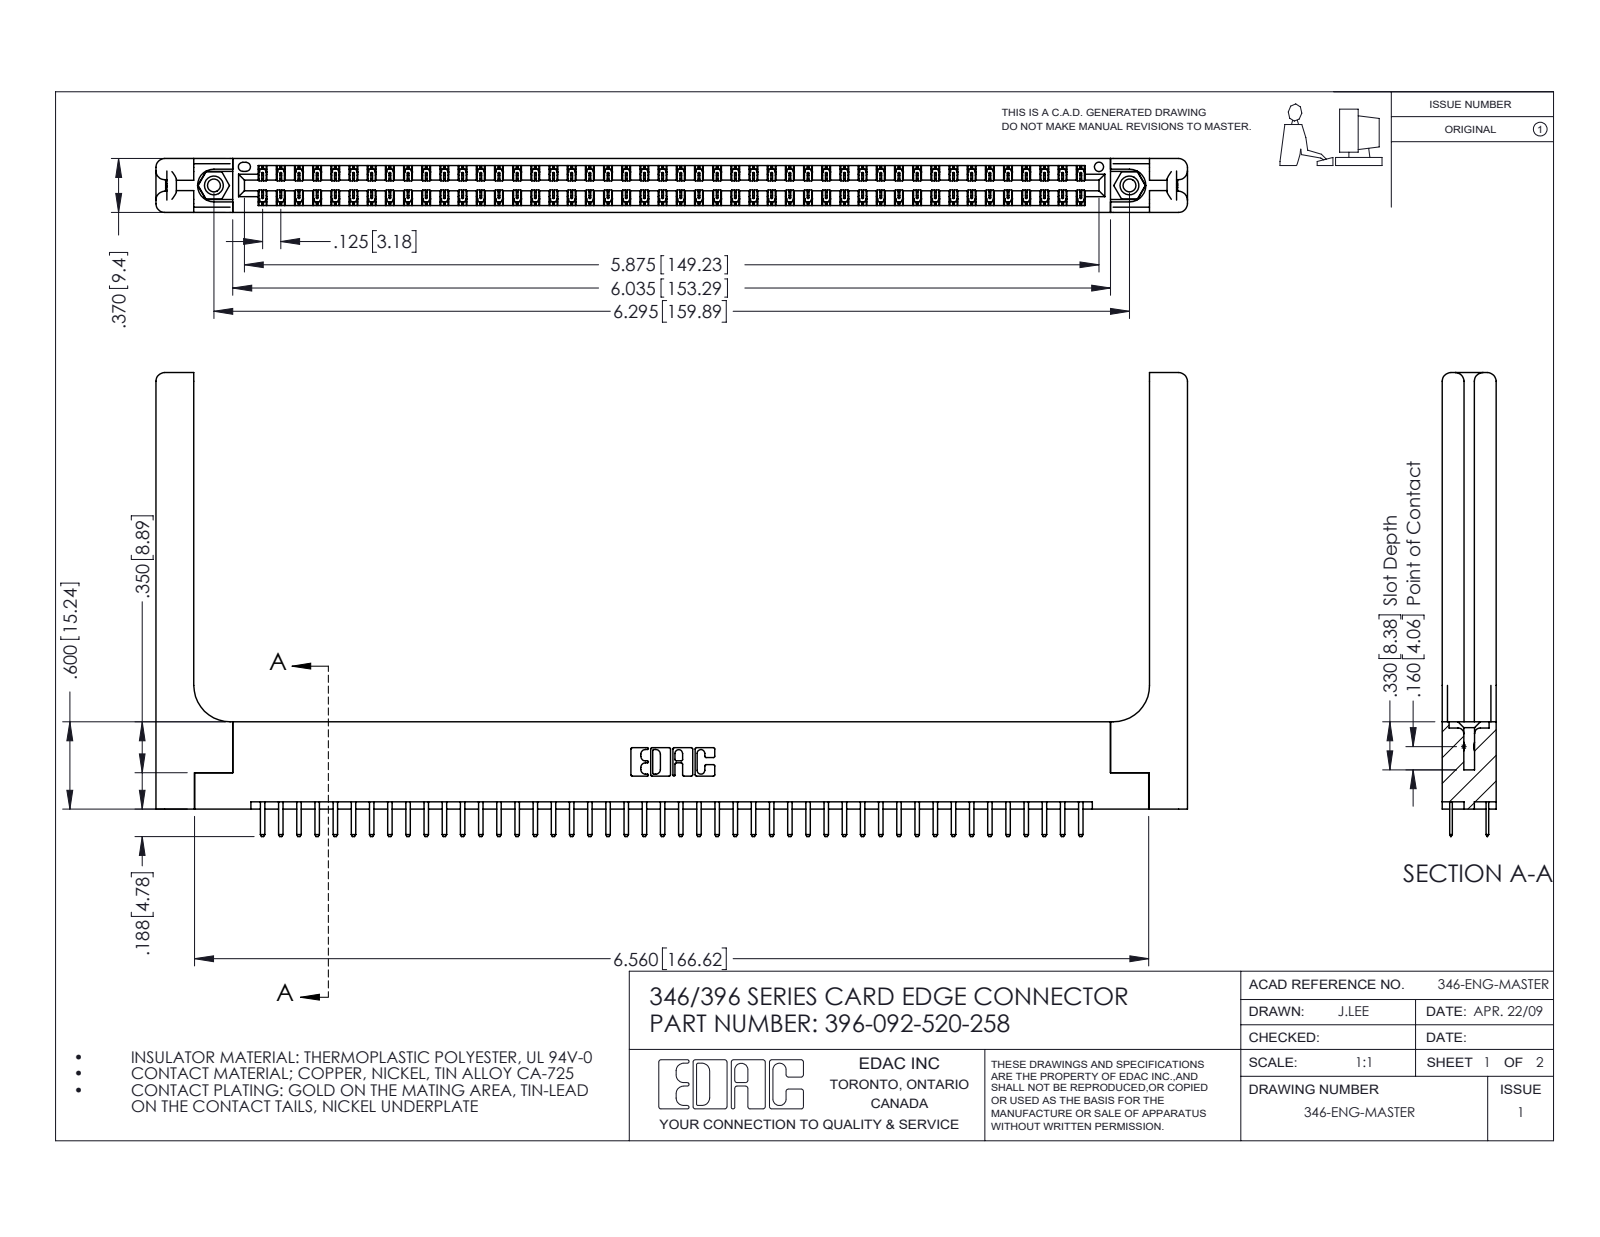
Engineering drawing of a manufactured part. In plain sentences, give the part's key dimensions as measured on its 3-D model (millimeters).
The part is named "345-250-001_345-250-001-102; 345-292-001_345-293-120; 346 Part_Flush Mounting Lugs - 0.156 Dia-TH; 396-092-520-258 (+1 more)". Its 3-D file was written by "SolidWorks 2016 (CONFIG_CONTROL_DESIGN)". It is 97 solids with 5530 faces: 3628 planar, 1842 cylindrical and 60 other. Overall it measures 180.1 by 81 by 9.4 millimeters. Its volume is 25 060 cubic millimeters and its surface area 29 070 square millimeters. Round holes: 2 of diameter 2.3, 2 of diameter 3.2, 2 of diameter 4, 1 of diameter 1.6. Round bosses or shafts: 2 of diameter 3.9. Partial cylindrical surfaces (rounded edges, fillets, slot ends): 138 of radius 0.2, 96 of radius 0.3, 22 of radius 0.3, 16 of radius 1.5, 6 of radius 0.2, 6 of radius 0.8, 3 of radius 0.7, 2 of radius 0.4. The main face-to-face distances are 9.4, 1.2, 8.2, 1.8, 6.4, 3.8, 3.8, 7.6, 0.6, 7. The hole center spacings are 6.2, 154.6, 159.9.
